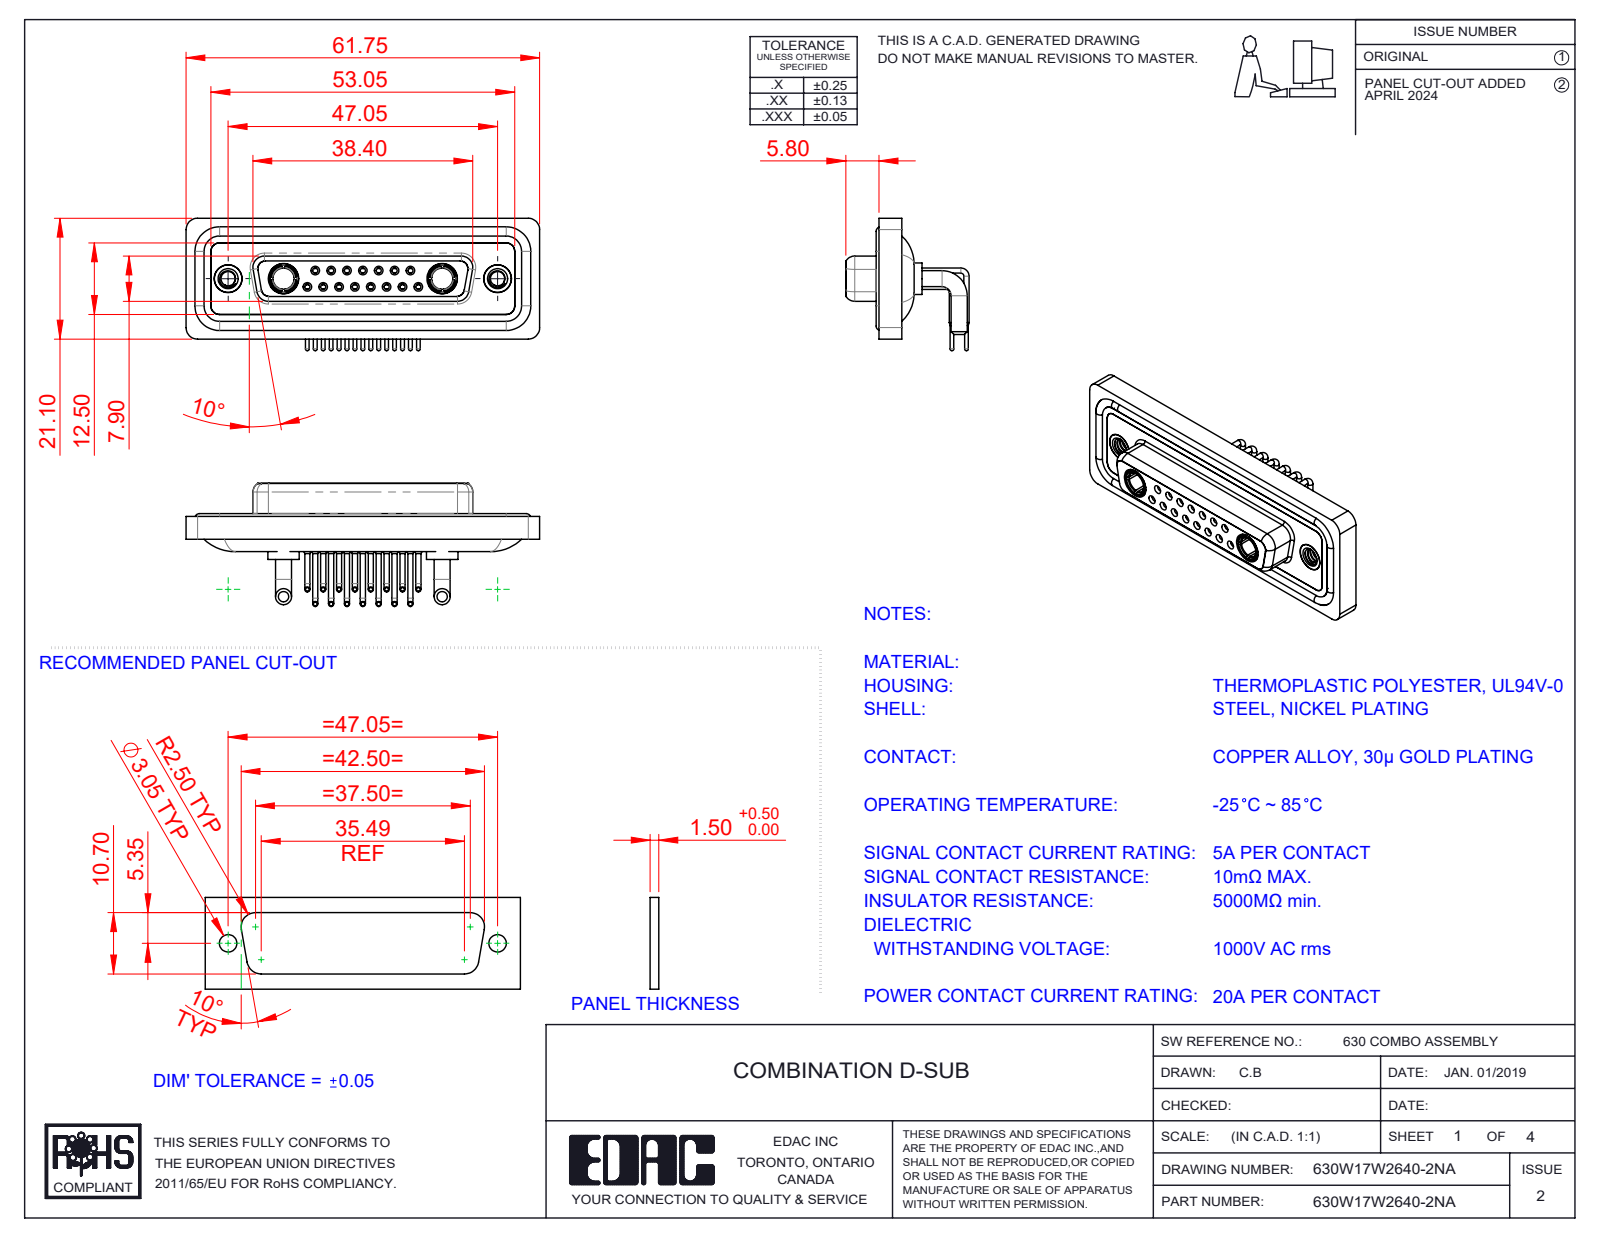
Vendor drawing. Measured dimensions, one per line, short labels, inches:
name: 630Combo Threaded Rivet_A; Power Socket_20A RA; 630Combo Contact Row 2_50 Contacts; 630Combo Waterproof Housing_25 Contacts (+5 more)
written by: SolidWorks 2023 (CONFIG_CONTROL_DESIGN)
unit: in
bodies: 26 solids, 1331 faces (388 planar, 581 cylindrical, 362 other)
size: 2.431 × 0.91 × 0.848
volume: 0.517 in³; area: 22.53 in²
holes: 15× ⌀0.035, 15× ⌀0.043, 15× ⌀0.059, 15× ⌀0.079, 8× ⌀0.063, 7× ⌀0.067, 4× ⌀0.191, 2× ⌀0.098, 2× ⌀0.146, 2× ⌀0.157, 2× ⌀0.159, 2× ⌀0.197
bosses: 15× ⌀0.035, 15× ⌀0.026, 11× ⌀0.063, 4× ⌀0.11, 2× ⌀0.217, 2× ⌀0.205, 2× ⌀0.195, 2× ⌀0.195
rounds: 18× R0.059, 18× R0.079, 8× R0.053, 8× R0.063, 4× R0.01, 4× R0.02, 4× R0.024, 4× R0.026
face distances: 0.016, 0.071, 0.161, 0.043, 0.063, 0.122, 0.059, 0.098, 0.146, 0.055
hole spacings: 0.124, 0.109, 0.218, 0.327, 0.198, 0.295, 0.436, 0.198
